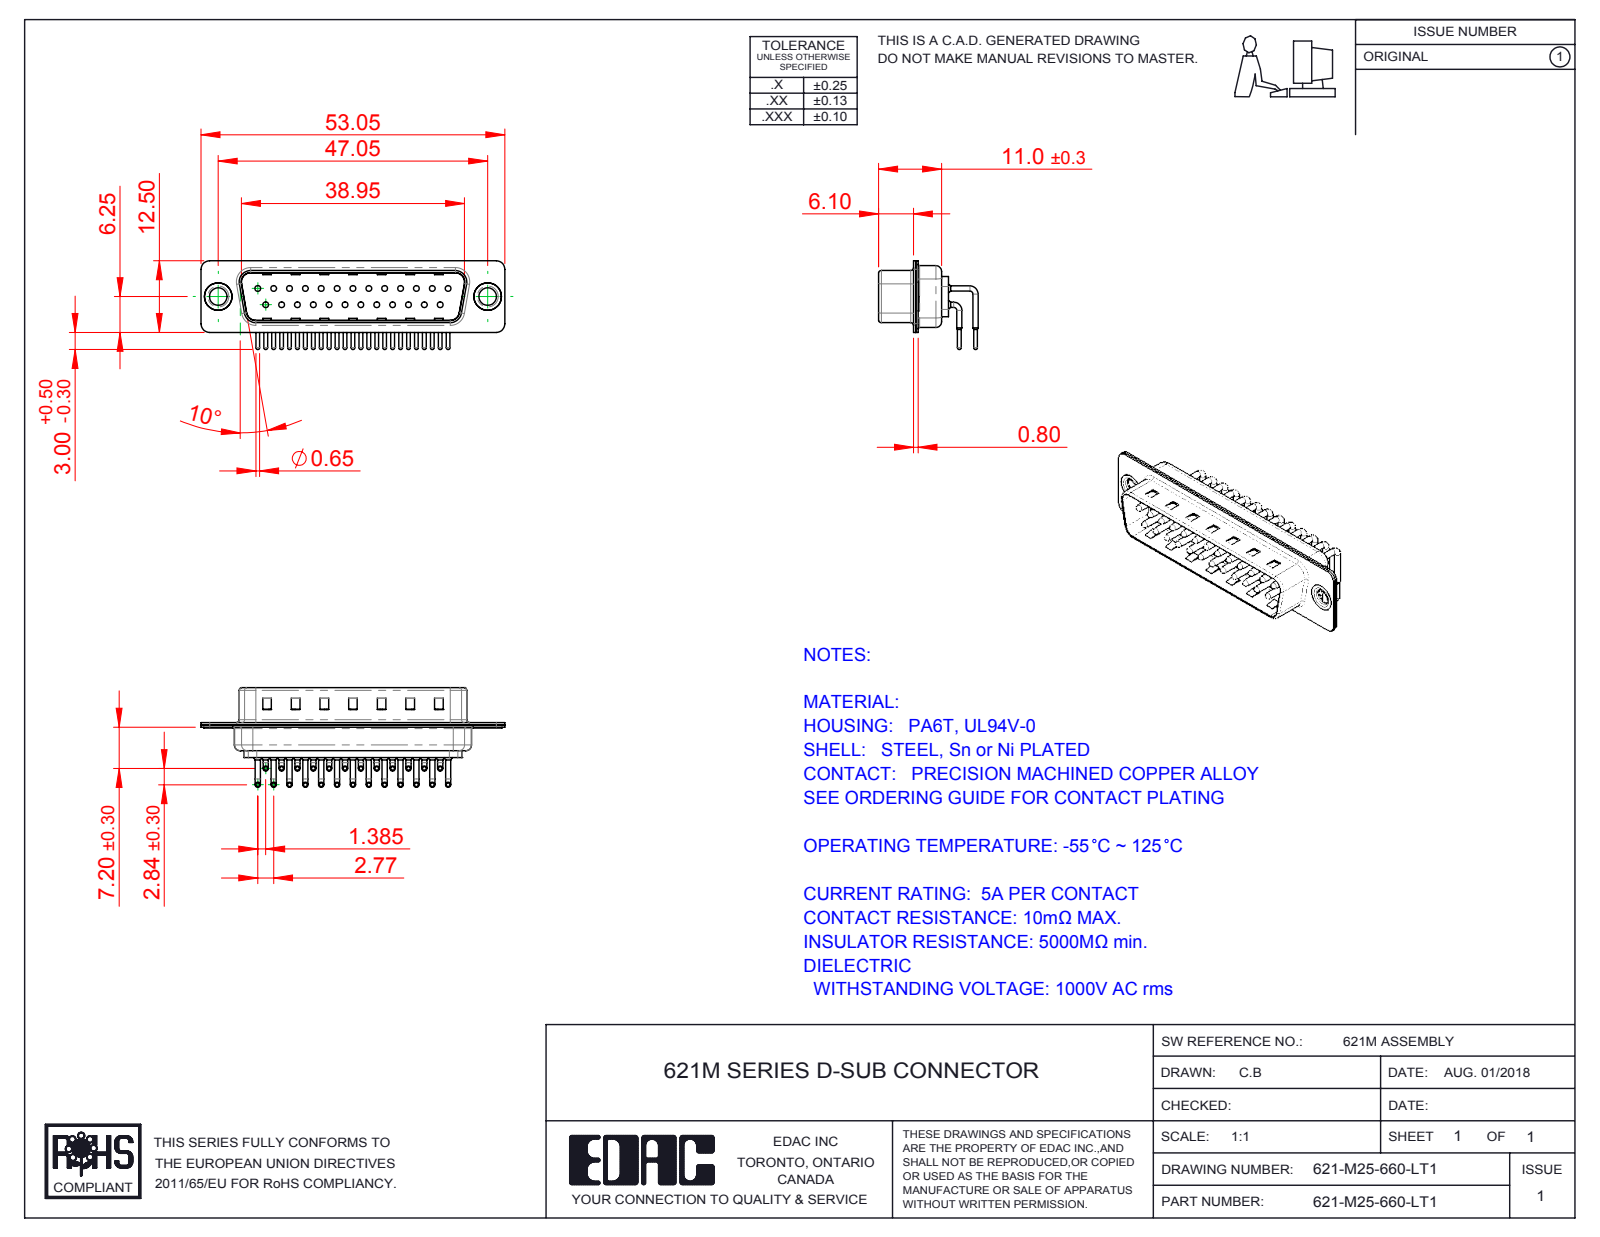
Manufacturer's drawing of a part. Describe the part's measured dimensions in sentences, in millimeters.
The part is named "621M Housing_25 Contacts; 621M Shell Rear_25 Contacts; 621M Shell Front_25 Contacts; 621M Contact Row 1 (+3 more)". Its 3-D file was written by "SolidWorks 2016 (CONFIG_CONTROL_DESIGN)". It is 30 solids with 3100 faces: 1771 planar, 1021 cylindrical and 308 other. Overall it measures 53.05 by 17.39 by 15.49 millimeters. Its volume is 2 796 cubic millimeters and its surface area 7 439 square millimeters. Round holes: 25 of diameter 1, 25 of diameter 1.7, 25 of diameter 2, 2 of diameter 3.05, 2 of diameter 4, 2 of diameter 4.8. Round bosses or shafts: 50 of diameter 0.9, 25 of diameter 1.5, 25 of diameter 0.65, 2 of diameter 5, 2 of diameter 4.9, 2 of diameter 3.55. Partial cylindrical surfaces (rounded edges, fillets, slot ends): 25 of radius 1.01, 16 of radius 1.5, 12 of radius 2, 8 of radius 0.5, 8 of radius 1.6, 4 of radius 0.25, 4 of radius 0.6, 4 of radius 0.65. The main face-to-face distances are 0.4, 0.85, 9.55, 8.7, 1.25, 10.4, 1.5, 1.9, 0.35, 6.1. The hole center spacings are 3.16, 8.31, 2.77, 5.54, 11.08, 16.62, 5.03, 5.04.
